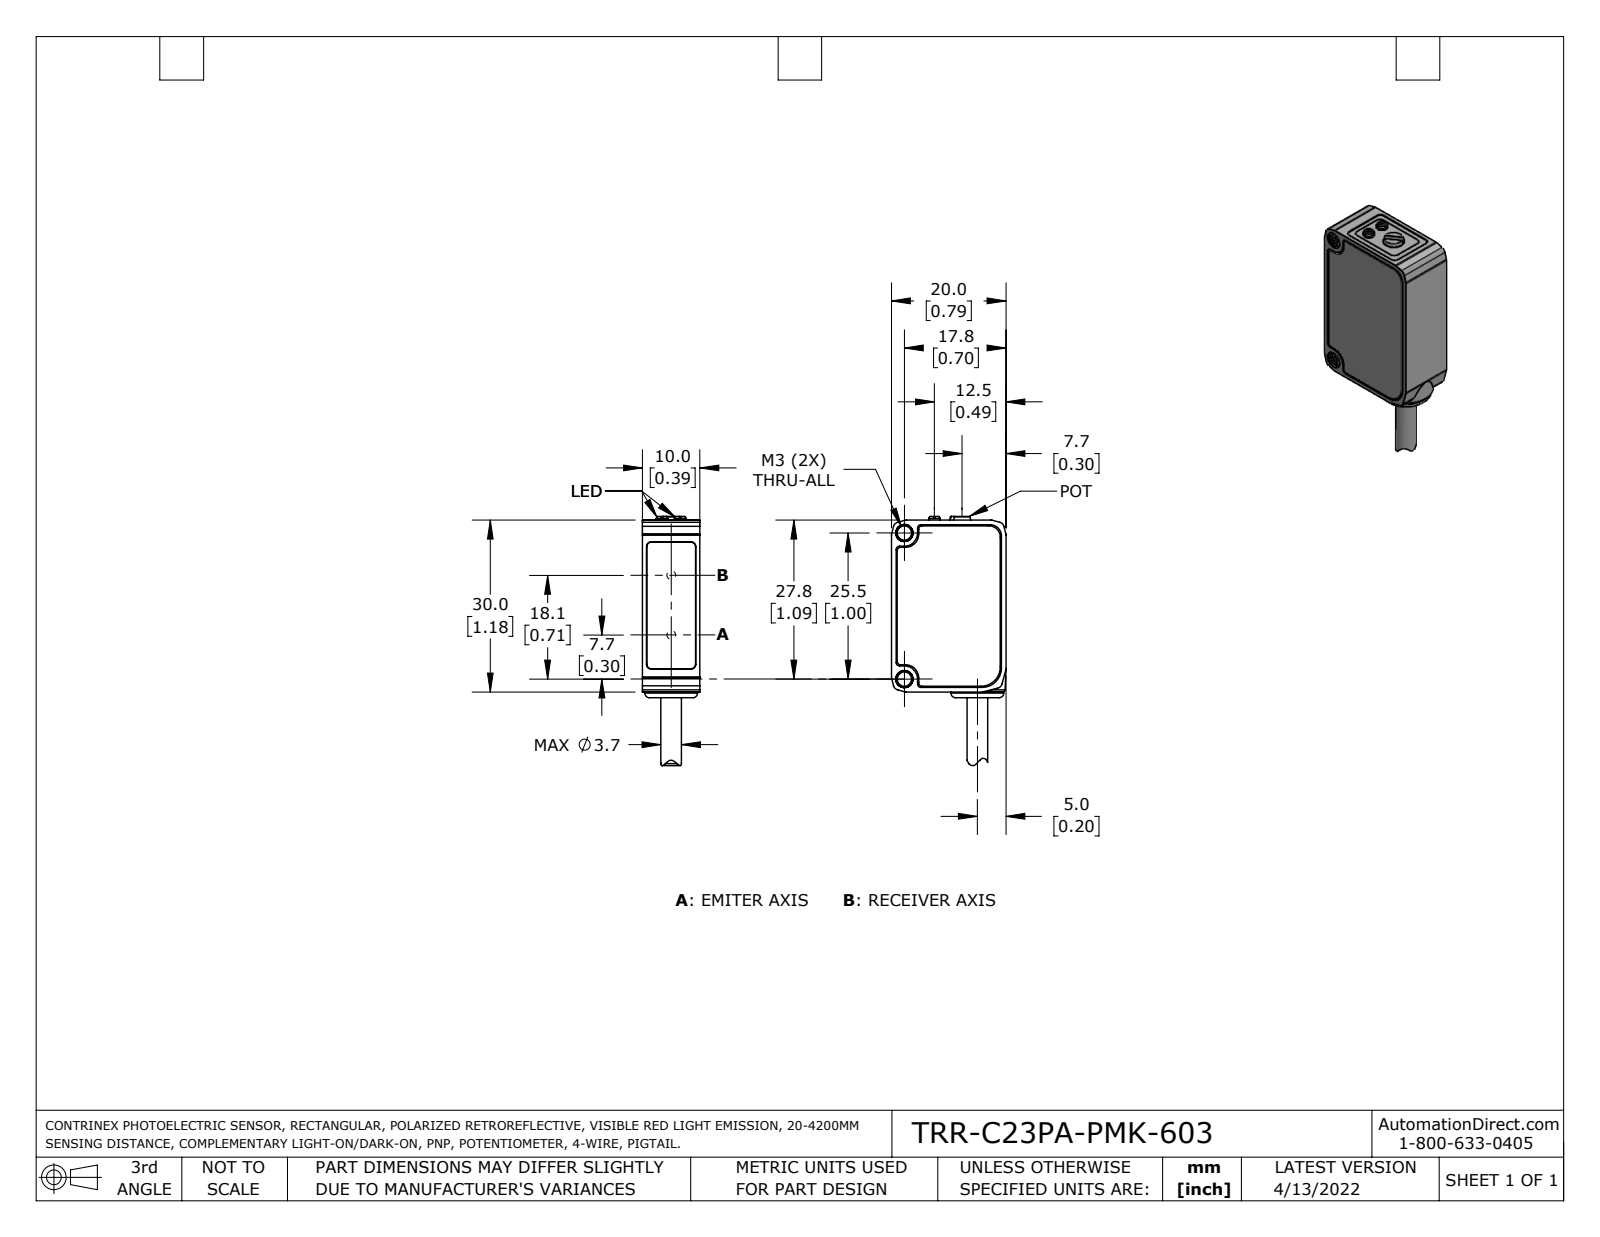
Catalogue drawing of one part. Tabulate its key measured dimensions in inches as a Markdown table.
| quantity | value |
| --- | --- |
| part name | TRR-C23PA-PMK-603 |
| STEP written by | SolidWorks 2021 (AUTOMOTIVE_DESIGN) |
| units | inches |
| bodies | 1 solid, 274 faces (91 planar, 136 cylindrical, 47 other) |
| overall size | 1.713 × 0.787 × 0.394 |
| volume | 0.365 in³ |
| surface area | 4.153 in² |
| round holes (diameter × count) | 0.098 × 2, 0.142 × 2 |
| round bosses / shafts (diameter × count) | 0.079 × 2, 0.362 × 1, 0.146 × 1, 0.142 × 1 |
| partial cylindrical surfaces (radius × count) | 0.031 × 20, 0.039 × 11, 0.024 × 8, 0.091 × 4, 0.134 × 3, 0.079 × 2, 0.025 × 1, 0.033 × 1 |
| main face-to-face distances | 0.394, 0.785, 0.039, 0.787, 1.181, 1.177, 0.028, 0.03, 1.179, 1.217 |
| hole center spacings | 1.004 |
